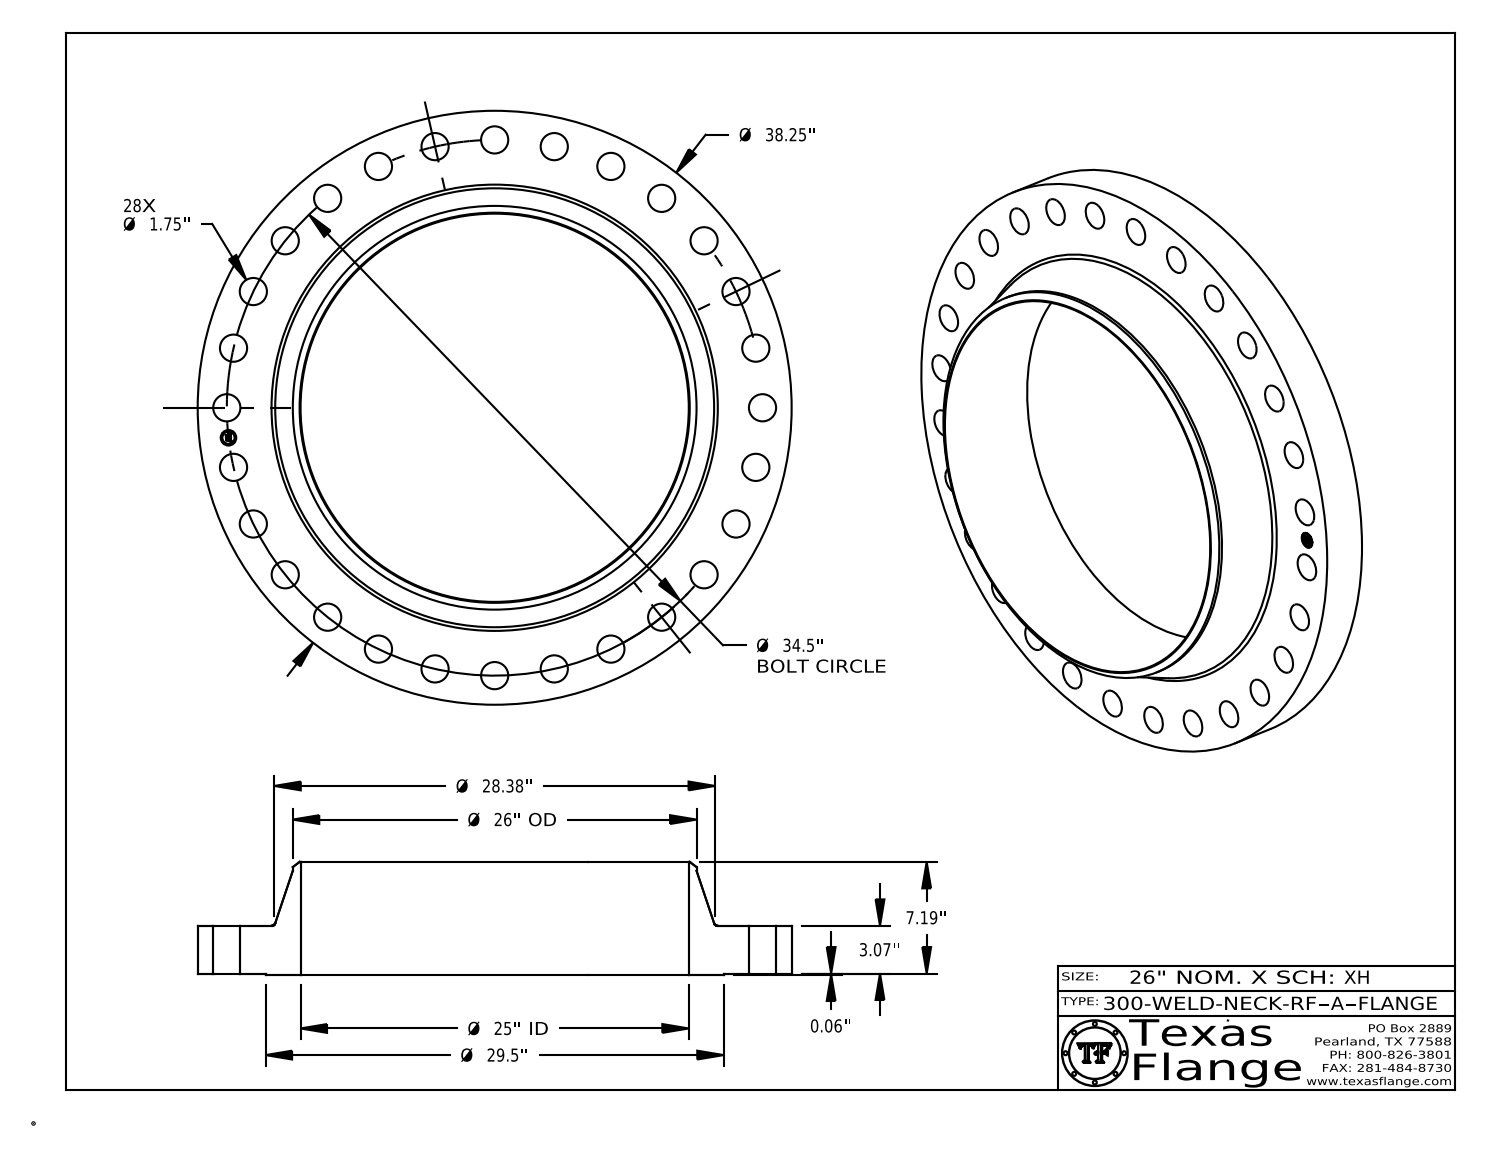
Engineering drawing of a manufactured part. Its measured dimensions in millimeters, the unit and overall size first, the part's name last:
Units: millimetres
Overall size (bounding box): 971.6 × 971.6 × 184.2
Round holes (diameter × count): ⌀44.5 ×28, ⌀25.4 ×1, ⌀635 ×1
Round bosses / shafts (diameter × count): ⌀1.5 ×8, ⌀971.6 ×1, ⌀749.3 ×1, ⌀660.4 ×1, ⌀20 ×1
Main face-to-face distances: 78, 1.6, 79.6, 184.2, 182.6, 104.6, 0.4, 79.2, 77.6, 105
Hole centre spacings: 438.2, 685.1, 870.8, 380.2, 466.2, 827.1, 854.3, 289.4
Volume: 35 450 000 mm³ · Surface area: 1 833 000 mm²
Bodies: 1 solid, 459 faces (369 planar, 84 cylindrical, 6 other)
Part name (STEP PRODUCT): 300-WELD-NECK-RF, Series A
STEP written by: CATIA V5 STEP AP214 (AUTOMOTIVE_DESIGN)
